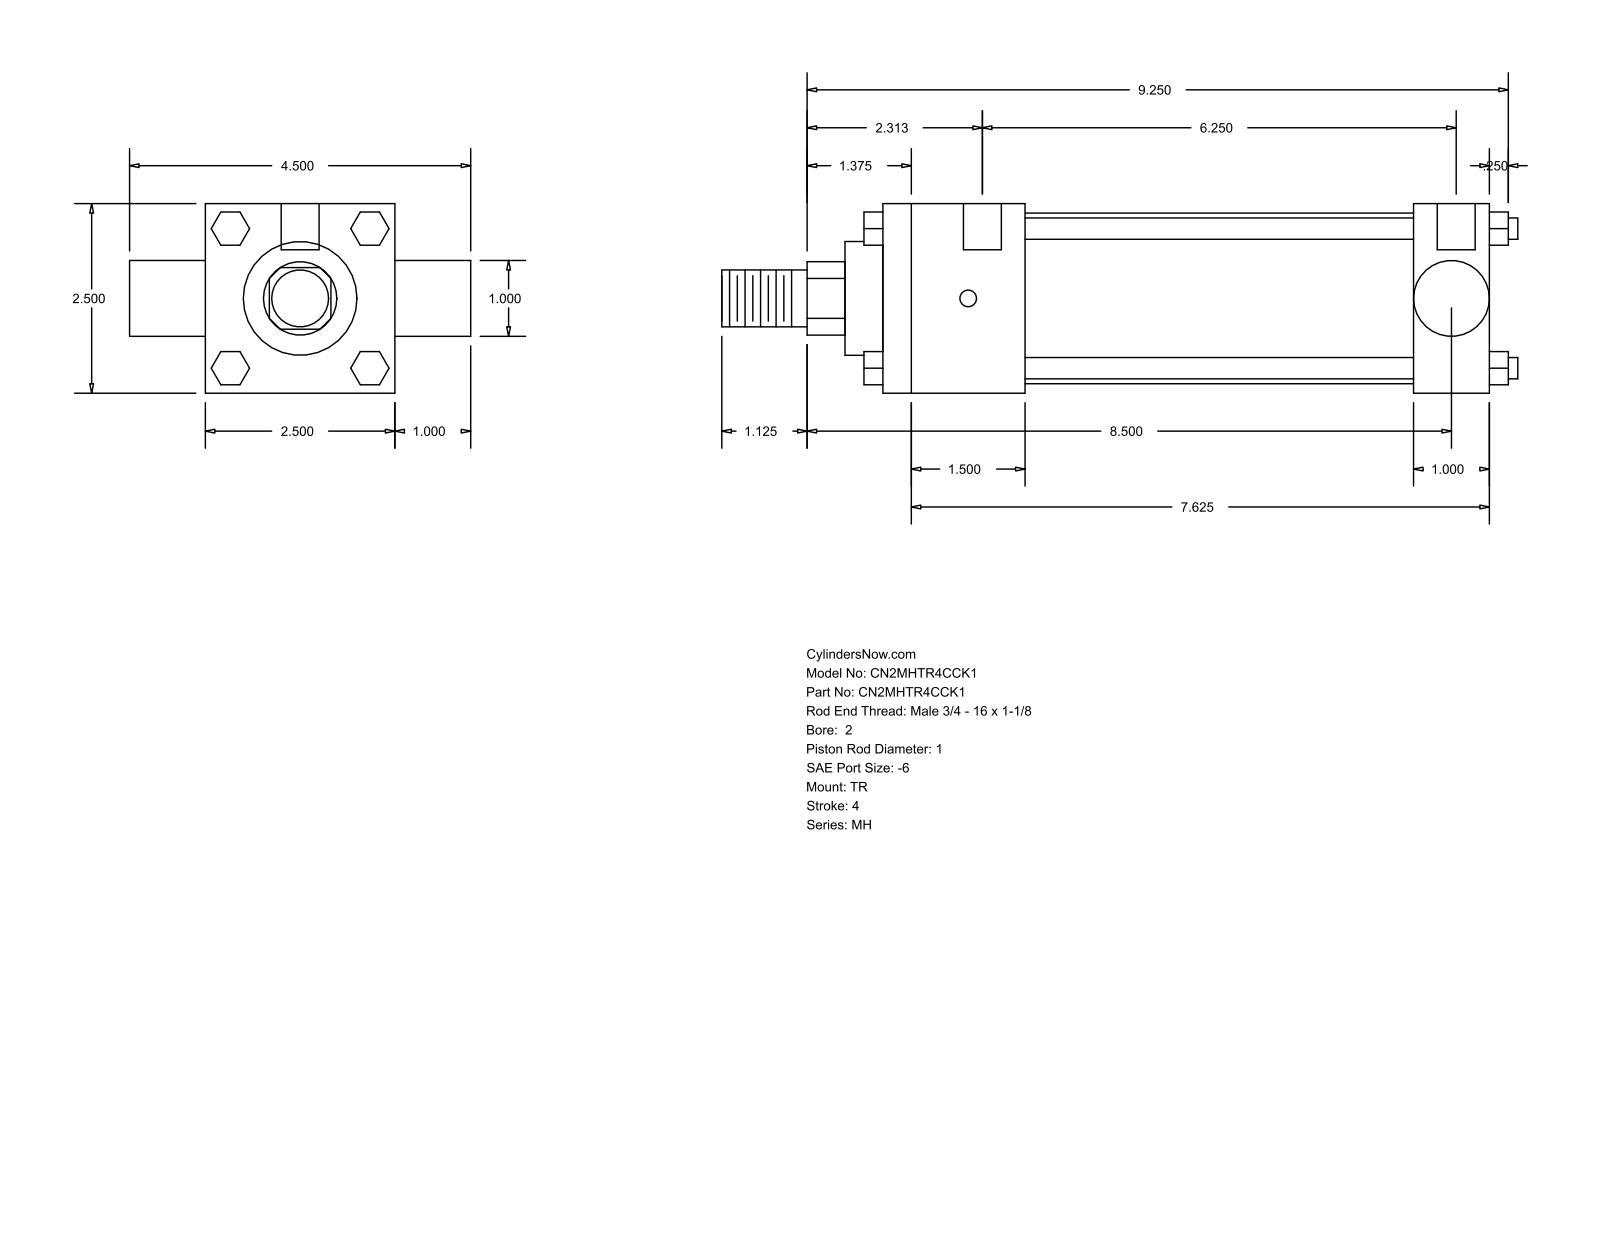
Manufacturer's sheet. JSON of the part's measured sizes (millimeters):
{"part_name": "MH_TR__0200_1", "step_written_by": "GSSL Pune (CONFIG_CONTROL_DESIGN)", "units": "millimeters", "bodies": {"solids": 0, "faces": 120, "planar": 92, "cylindrical": 28, "other": 0}, "overall_size": [266.7, 114.3, 63.5], "round_holes": [[5.56, 3], [12.7, 2]], "round_bosses_or_shafts": [[7.14, 4], [57.15, 1], [38.1, 1], [25.4, 1], [25.35, 1], [19.05, 1]], "partial_cylinders_radius": [[12.29, 1]], "face_to_face_distances": [63.5, 203.2, 25.4, 47.63, 177.8, 130.17, 155.57, 88.9, 215.9, 6.35], "hole_center_spacings": [3.17, 4.76, 158.75, 161.92, 163.51, 166.68]}
